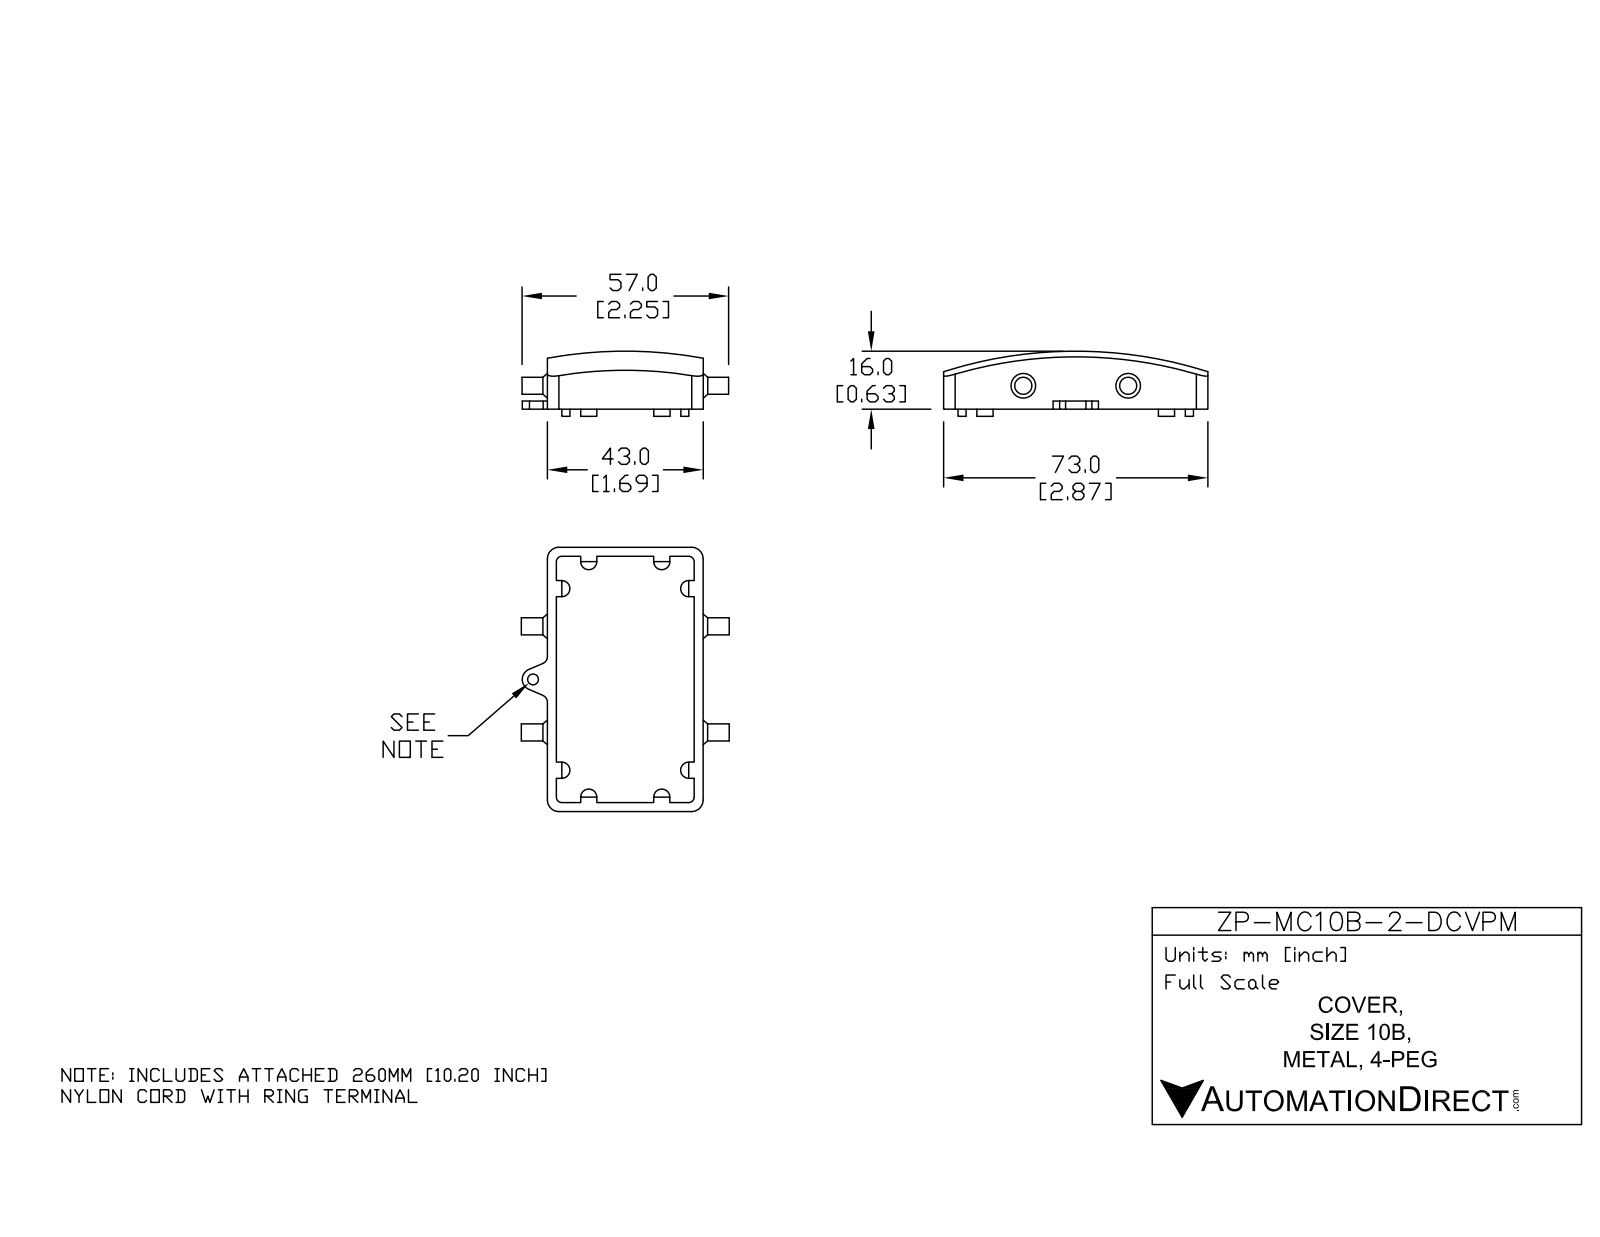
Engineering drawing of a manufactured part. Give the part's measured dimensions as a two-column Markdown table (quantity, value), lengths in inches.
| quantity | value |
| --- | --- |
| part name | ZP-MC10B-2-DCVPM |
| STEP written by | SolidWorks 2011 (AUTOMOTIVE_DESIGN) |
| units | inches |
| bodies | 1 solid, 86 faces (56 planar, 24 cylindrical, 6 other) |
| overall size | 2.894 × 2.283 × 0.728 |
| volume | 0.934 in³ |
| surface area | 19.29 in² |
| round holes (diameter × count) | 0.118 × 1 |
| round bosses / shafts (diameter × count) | 0.187 × 2 |
| partial cylindrical surfaces (radius × count) | 0.089 × 8, 0.028 × 4, 0.126 × 4, 0.079 × 2, 0.118 × 1 |
| main face-to-face distances | 0.098, 1.614, 1.713, 1.516, 2.795, 2.894, 2.697, 0.443, 0.384, 0.541 |
